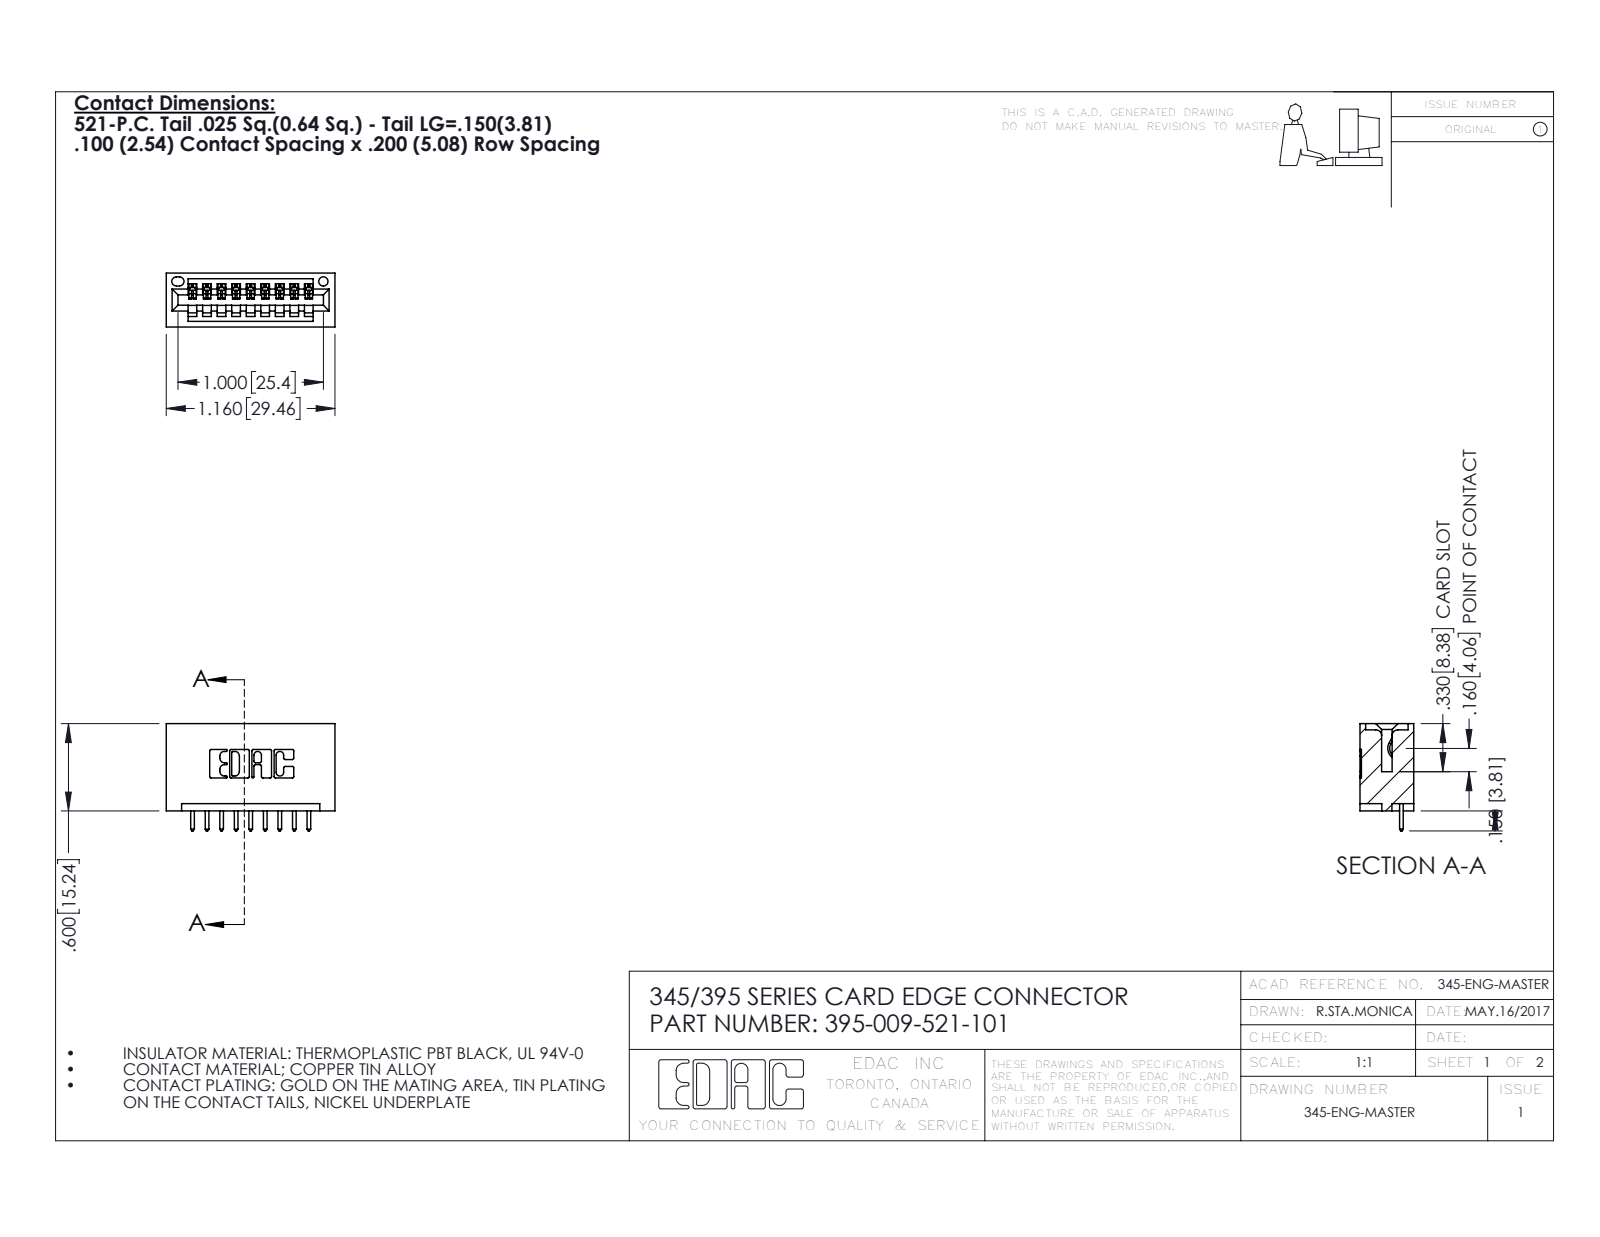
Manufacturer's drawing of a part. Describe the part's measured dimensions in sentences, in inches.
The part is named "345-292-001_345-293-121; 395-009-521-101; 345 Part_No Mounting Lugs". Its 3-D file was written by "SolidWorks 2016 (CONFIG_CONTROL_DESIGN)". It is 10 solids with 640 faces: 436 planar, 204 cylindrical and 0 other. Overall it measures 1.16 by 0.737 by 0.37 inches. Its volume is 0.188 cubic inches and its surface area 5.803 square inches. Round holes: 1 of diameter 0.064. Partial cylindrical surfaces (rounded edges, fillets, slot ends): 22 of radius 0.01, 18 of radius 0.006, 18 of radius 0.01, 6 of radius 0.007, 6 of radius 0.031, 3 of radius 0.026, 2 of radius 0.031, 2 of radius 0.04. The main face-to-face distances are 0.2, 0.1, 0.298, 0.072, 0.37, 0.3, 0.4, 0.098, 0.272, 0.025.
